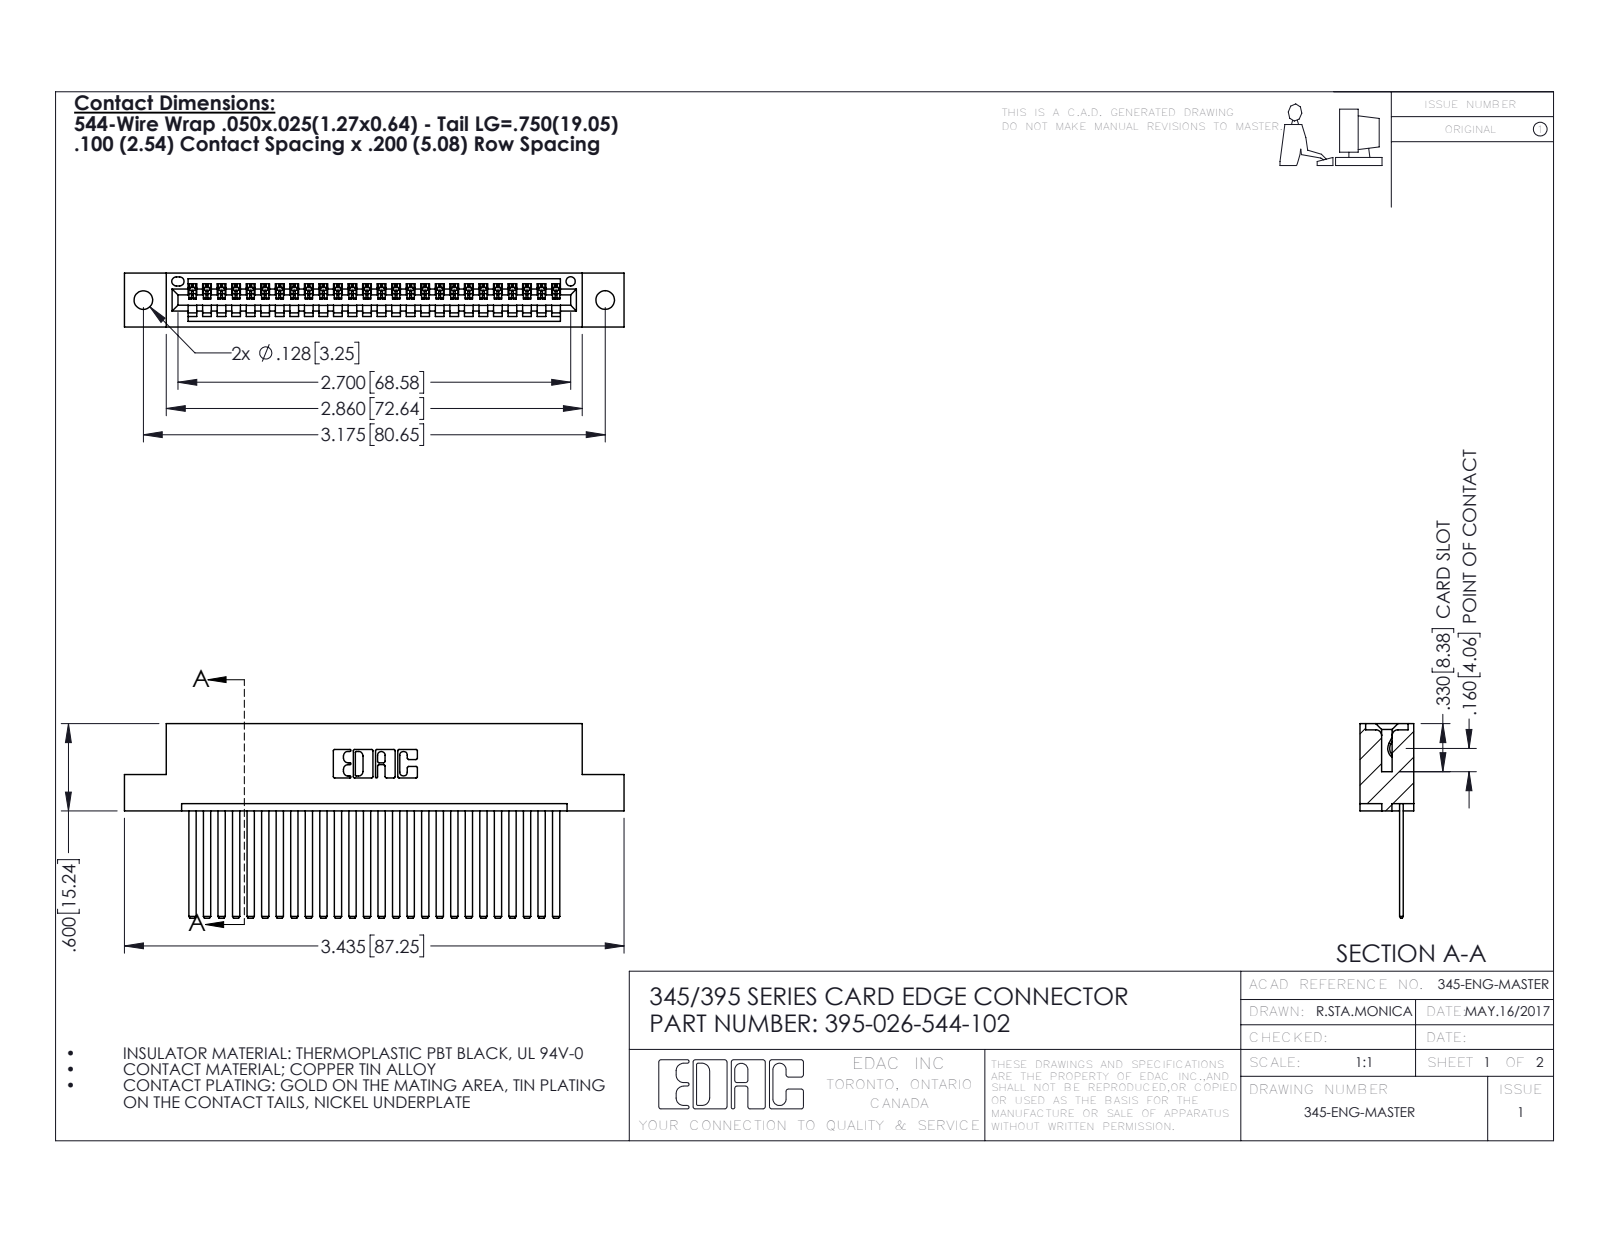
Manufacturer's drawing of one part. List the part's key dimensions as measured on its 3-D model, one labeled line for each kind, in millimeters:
Part name (STEP PRODUCT): 395-026-544-102; 345-292-001_345-293-144; 345 Part_Flush Mounting Lugs - 0.128 Dia
STEP written by: SolidWorks 2016 (CONFIG_CONTROL_DESIGN)
Units: millimetres
Bodies: 27 solids, 1478 faces (1016 planar, 462 cylindrical, 0 other)
Overall size (bounding box): 87.2 × 34 × 9.4
Volume: 8 420 mm³ · Surface area: 11 610 mm²
Round holes (diameter × count): ⌀3.3 ×2, ⌀1.6 ×1
Partial cylindrical surfaces — rounded edges, fillets, slot ends (radius × count): R0.2 ×52, R0.3 ×22, R0.2 ×6, R0.8 ×6, R0.7 ×3, R0.8 ×2, R1 ×2, R0.4 ×1
Main face-to-face distances: 1.8, 7.6, 2.5, 0.6, 6.9, 5.1, 9.4, 5.7, 3.8, 1.8
Hole centre spacings: 6.9, 74.7, 80.6
